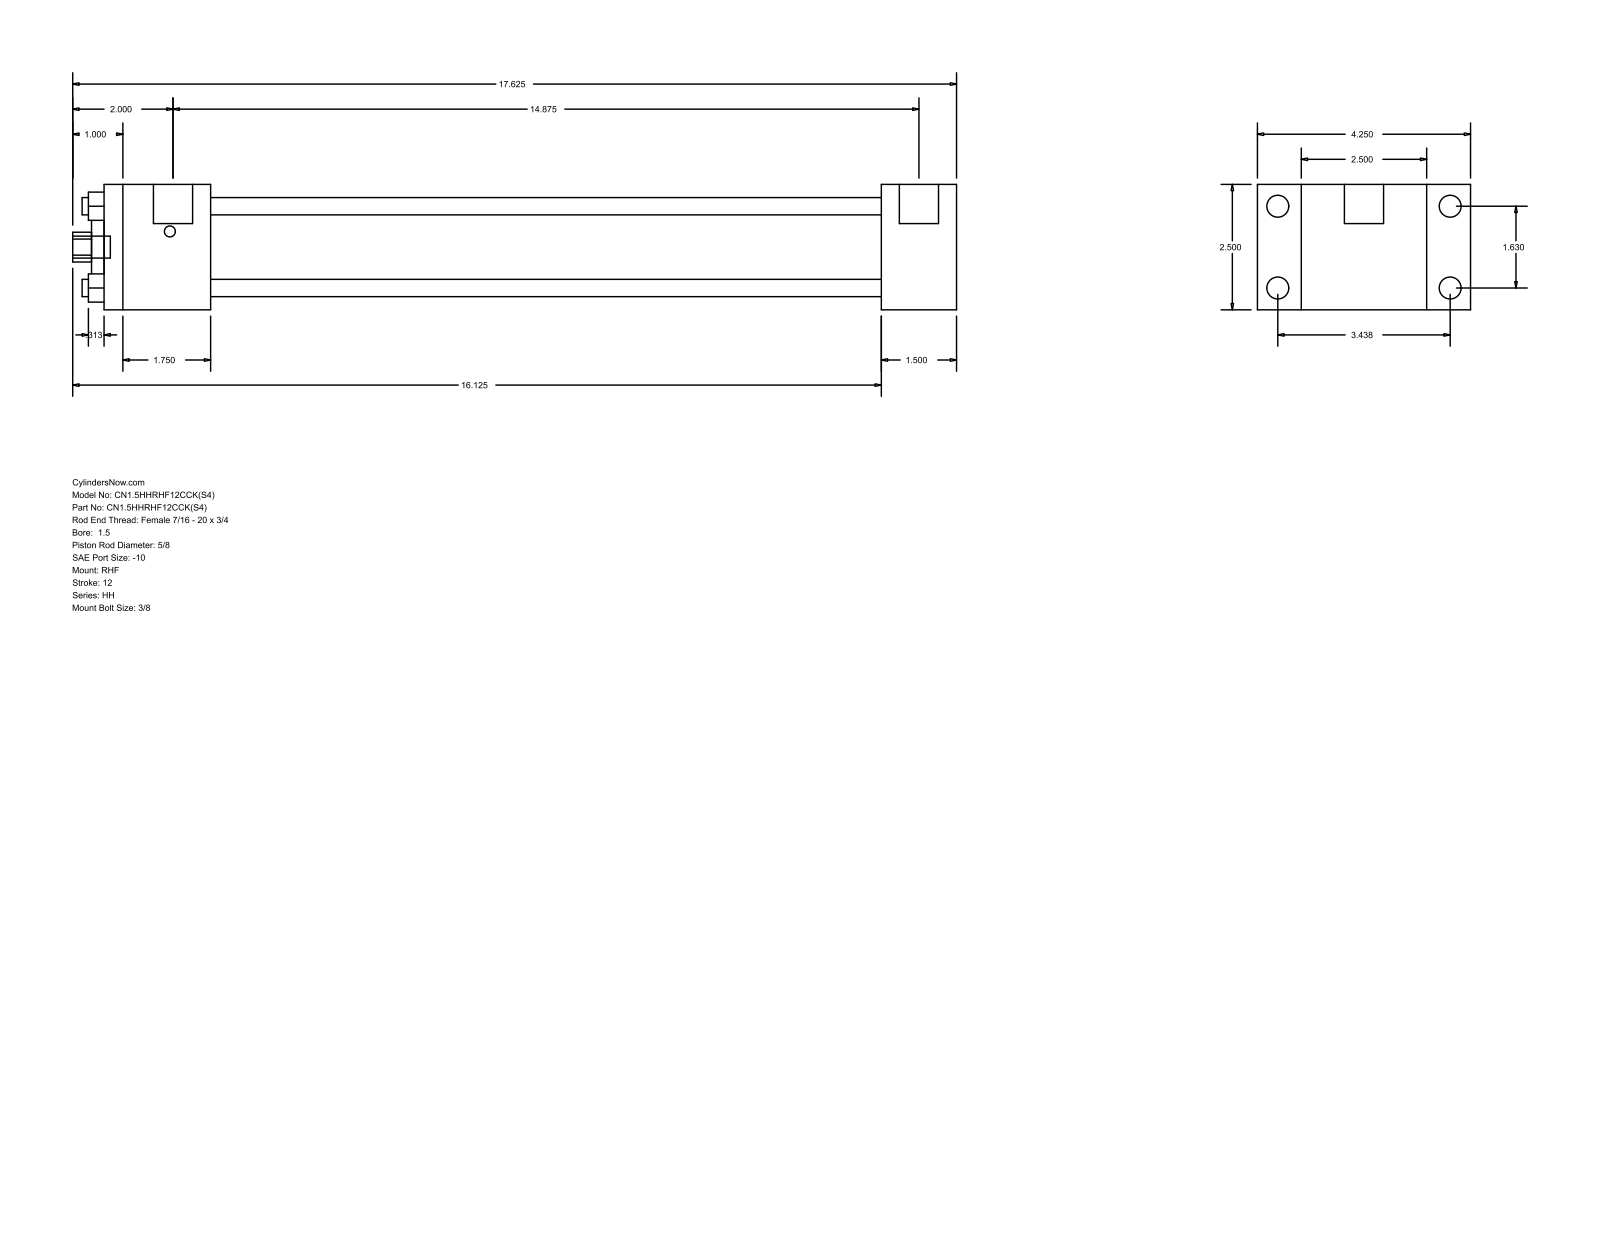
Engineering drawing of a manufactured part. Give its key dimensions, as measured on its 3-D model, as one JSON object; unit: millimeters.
{"part_name": "HH_RHF__0150_0.625", "step_written_by": "GSSL Pune (CONFIG_CONTROL_DESIGN)", "units": "millimeters", "bodies": {"solids": 0, "faces": 88, "planar": 60, "cylindrical": 28, "other": 0}, "overall_size": [447.68, 107.95, 63.5], "round_holes": [[8.76, 4], [15.88, 1], [28.57, 1], [44.45, 1]], "round_bosses_or_shafts": [[11.13, 4], [5.56, 4], [19.84, 2], [11.11, 1]], "partial_cylinders_radius": [[7.54, 1]], "face_to_face_distances": [63.5, 22.23, 85.73, 38.11, 393.69, 431.8, 107.96, 53.97, 339.72, 377.83], "hole_center_spacings": [29.27, 41.4, 58.55]}
